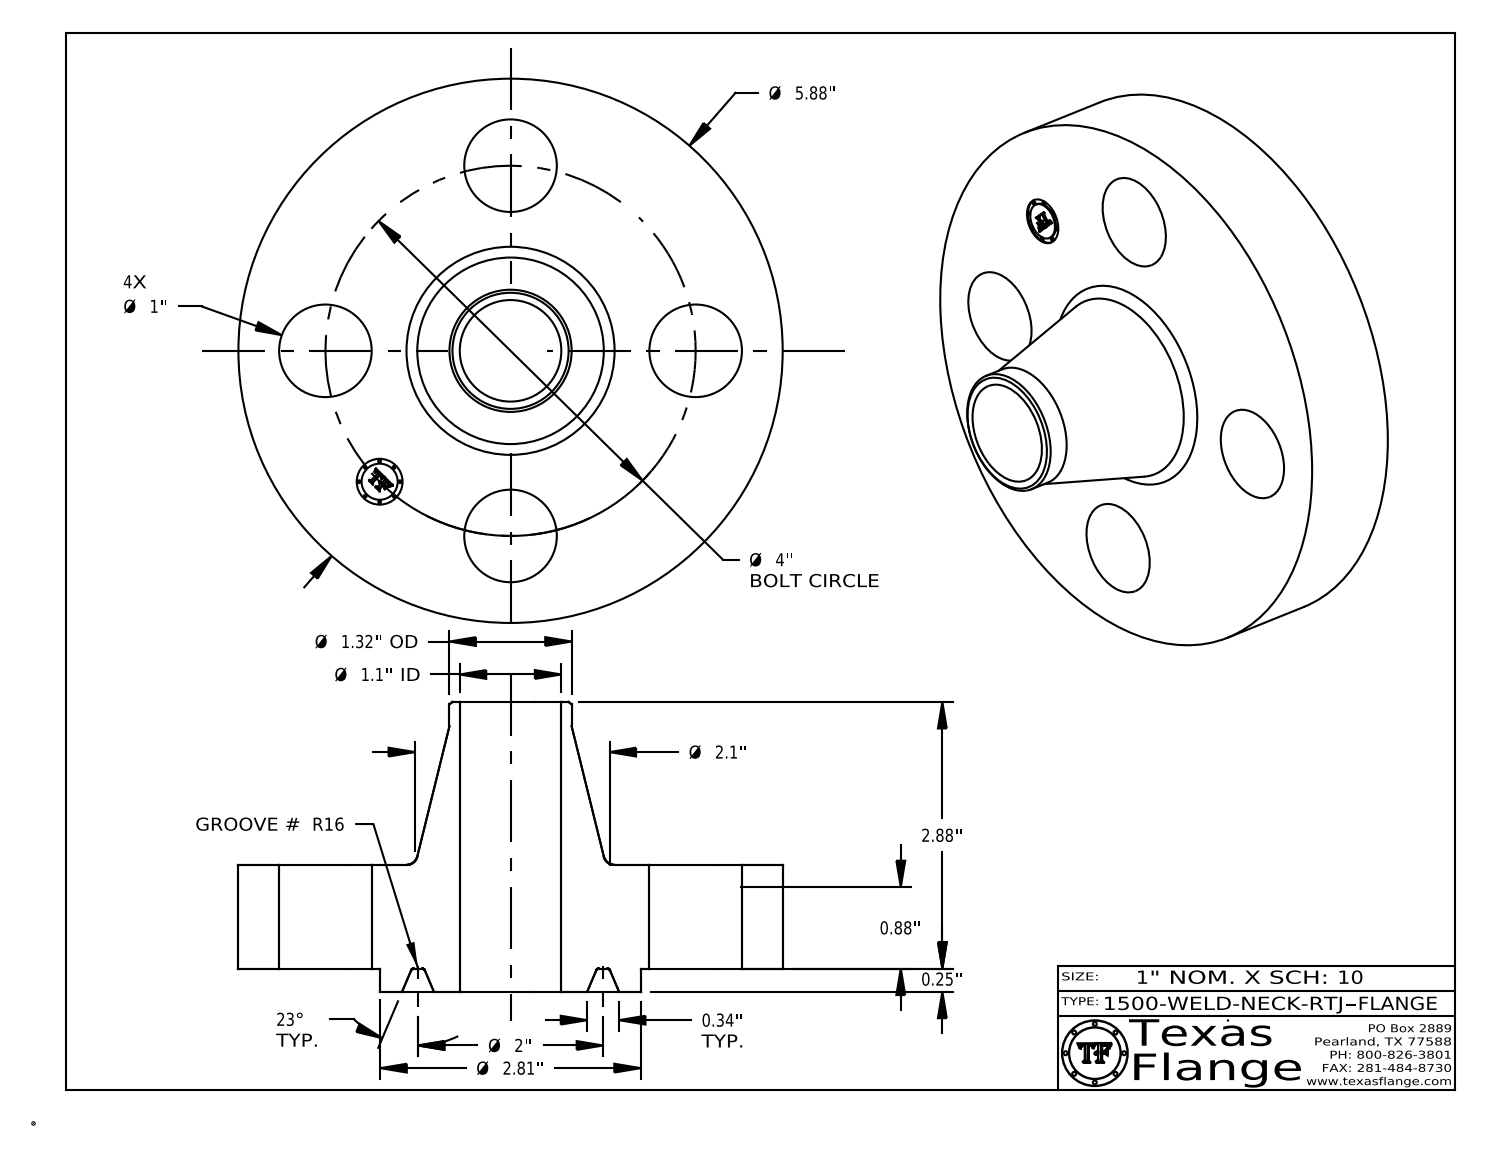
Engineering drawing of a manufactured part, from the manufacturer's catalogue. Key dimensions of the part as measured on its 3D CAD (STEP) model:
Part name (STEP PRODUCT): 1500-WELD-NECK-RTJ
STEP written by: CATIA V5 STEP AP214 (AUTOMOTIVE_DESIGN)
Units: inches
Bodies: 1 solid, 421 faces (371 planar, 36 cylindrical, 14 other)
Overall size (bounding box): 5.88 × 5.88 × 3.13
Volume: 28.9 in³ · Surface area: 103.1 in²
Round holes (diameter × count): ⌀1 ×4, ⌀0.495 ×1, ⌀1.097 ×1
Round bosses / shafts (diameter × count): ⌀0.03 ×8, ⌀5.88 ×1, ⌀2.813 ×1, ⌀1.32 ×1, ⌀0.39 ×1
Main face-to-face distances: 1.12, 0.25, 1.37, 3.13, 2.88, 1.76, 0.015, 1.355, 1.105, 1.775
Hole centre spacings: 2, 2.828, 1.531, 3.695, 4
